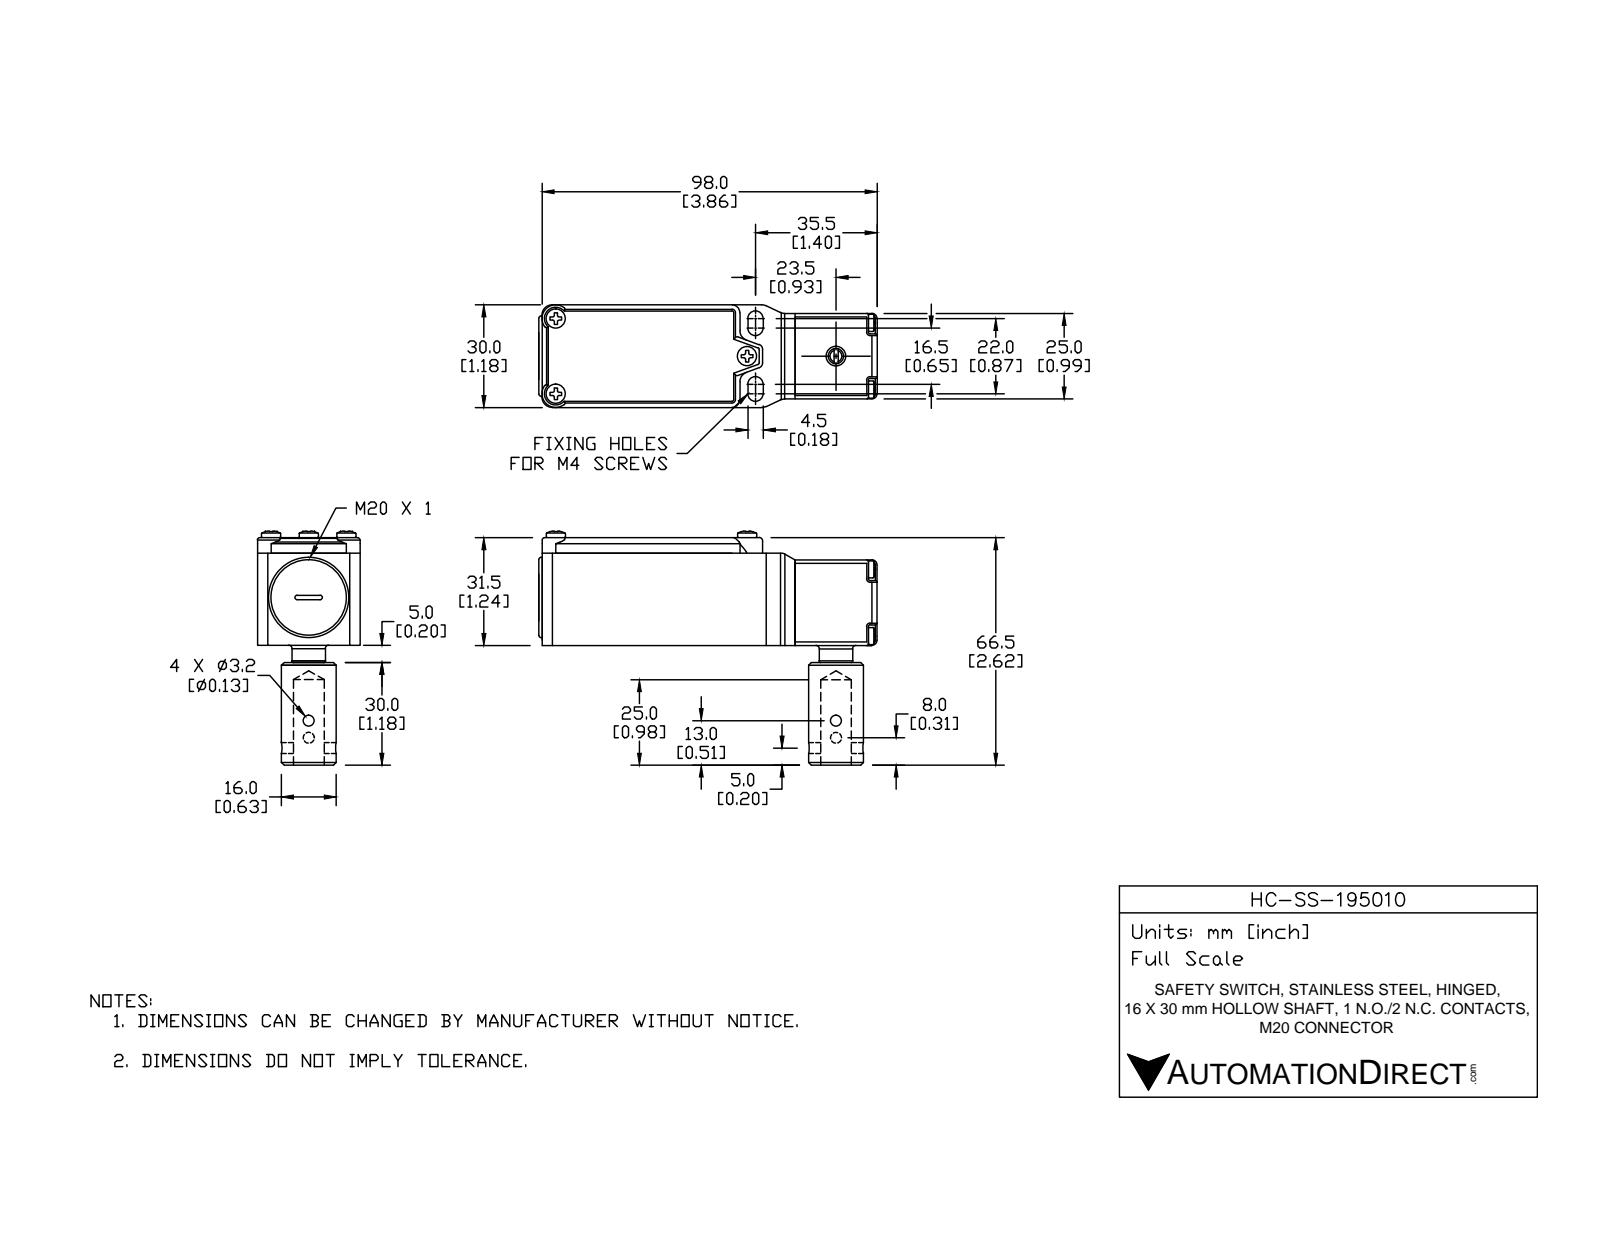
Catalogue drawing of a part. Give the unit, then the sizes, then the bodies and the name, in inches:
Units: inches
Overall size (bounding box): 3.898 × 2.694 × 1.181
Round holes (diameter × count): ⌀0.126 ×10, ⌀0.098 ×8, ⌀0.157 ×3, ⌀0.059 ×2, ⌀0.071 ×2, ⌀0.087 ×2, ⌀0.142 ×2, ⌀0.081 ×1, ⌀0.114 ×1, ⌀0.173 ×1, ⌀0.185 ×1, ⌀0.217 ×1
Round bosses / shafts (diameter × count): ⌀0.118 ×7, ⌀0.197 ×5, ⌀0.138 ×4, ⌀0.22 ×3, ⌀0.925 ×1, ⌀0.697 ×1, ⌀0.63 ×1, ⌀0.386 ×1
Partial cylindrical surfaces — rounded edges, fillets, slot ends (radius × count): R0.02 ×175, R0.039 ×20, R0.012 ×18, R0.006 ×14, R0.028 ×8, R0.118 ×8, R0.059 ×6, R0.089 ×4
Main face-to-face distances: 0.098, 1.142, 0.079, 1.181, 0.114, 1.067, 0.177, 1.24, 0.016, 1.043
Hole centre spacings: 0.543, 0.768, 0.187, 0.245, 0.414, 0.423, 0.426, 0.476
Volume: 2.656 in³ · Surface area: 54.51 in²
Bodies: 13 solids, 1182 faces (347 planar, 476 cylindrical, 359 other)
Part name (STEP PRODUCT): HC-SS-195010
STEP written by: SolidWorks 2014 (AUTOMOTIVE_DESIGN)
